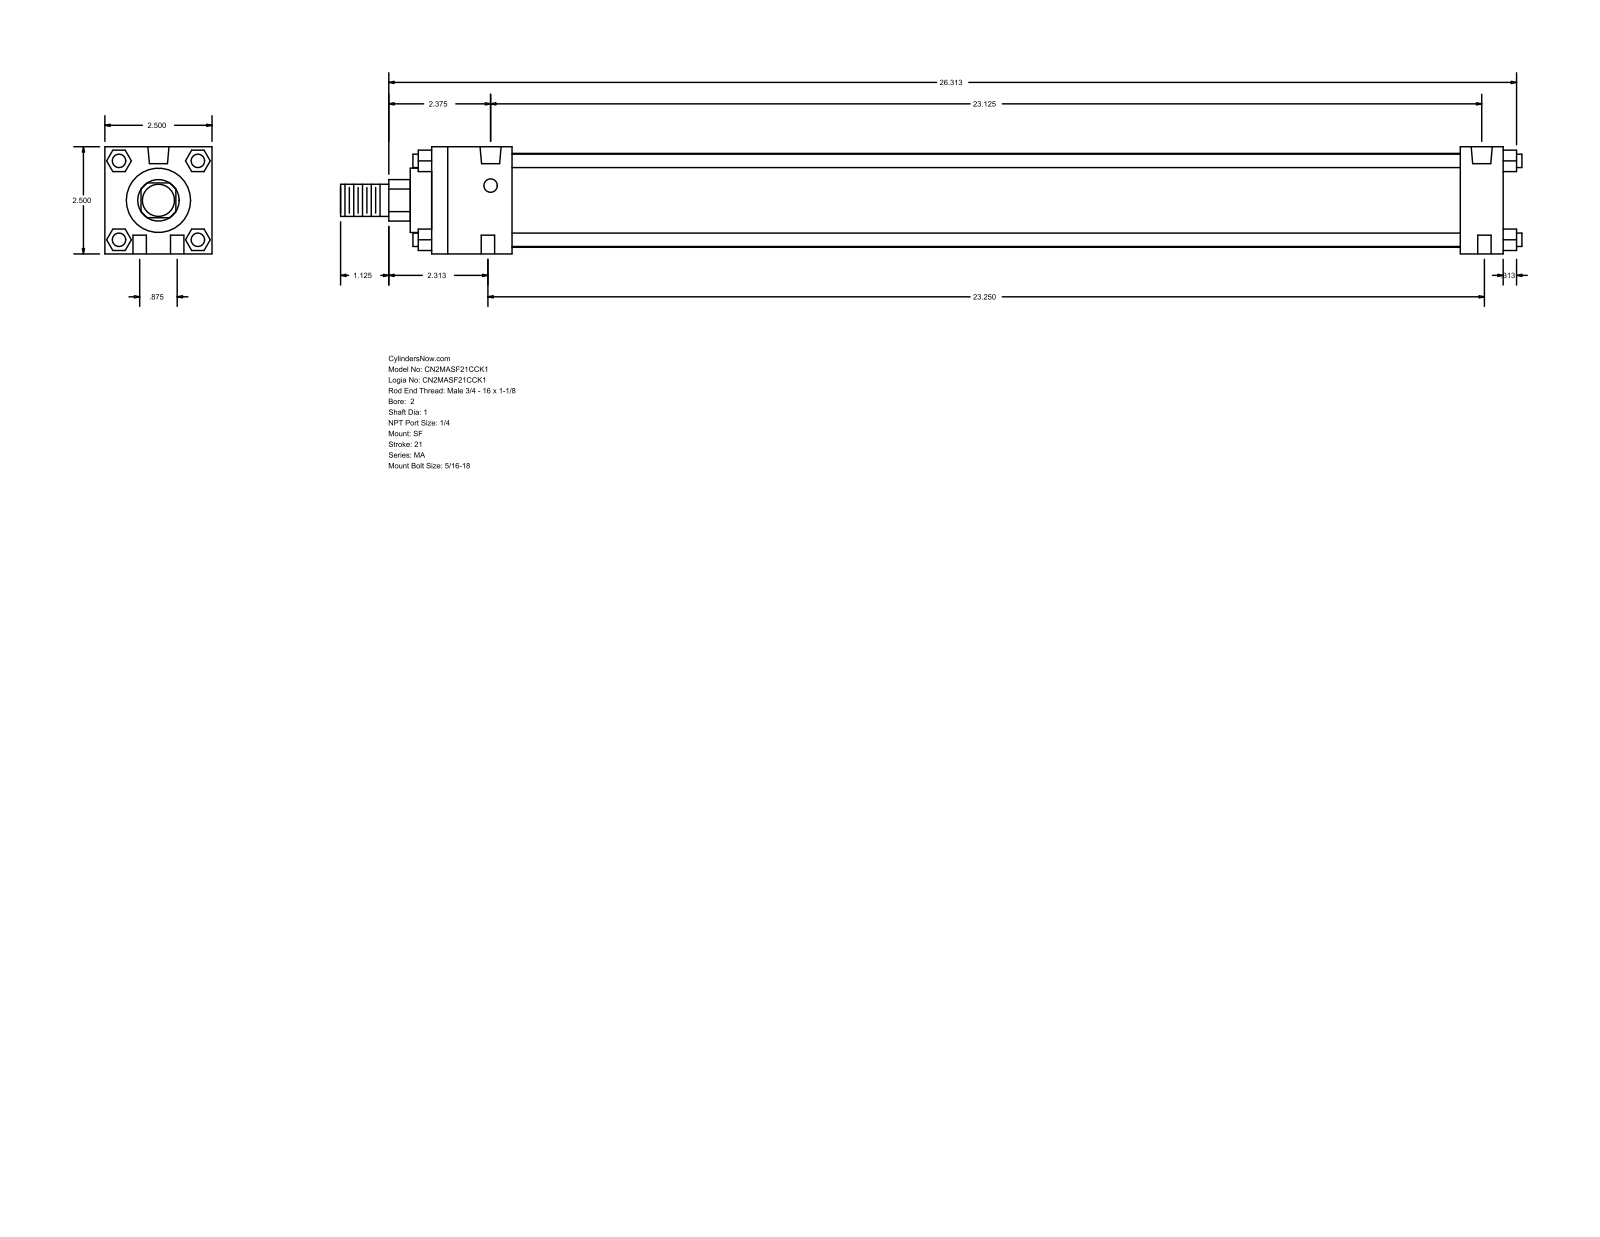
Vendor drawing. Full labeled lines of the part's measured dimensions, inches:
Part name (STEP PRODUCT): MA_SF__0200_1
STEP written by: GSSL Pune (CONFIG_CONTROL_DESIGN)
Units: inches
Bodies: 0 solids, 124 faces (94 planar, 30 cylindrical, 0 other)
Overall size (bounding box): 27.563 × 2.5 × 2.5
Round holes (diameter × count): ⌀0.313 ×6, ⌀0.492 ×2
Round bosses / shafts (diameter × count): ⌀0.313 ×4, ⌀2.19 ×1, ⌀1.5 ×1, ⌀1 ×1, ⌀0.75 ×1
Partial cylindrical surfaces — rounded edges, fillets, slot ends (radius × count): R0.484 ×1
Main face-to-face distances: 2.5, 25, 0.5, 1, 24, 1.875, 22.125, 23.125, 1.593, 0.92
Hole centre spacings: 0.442, 23.191, 0.875, 23.125, 23.25, 23.267
